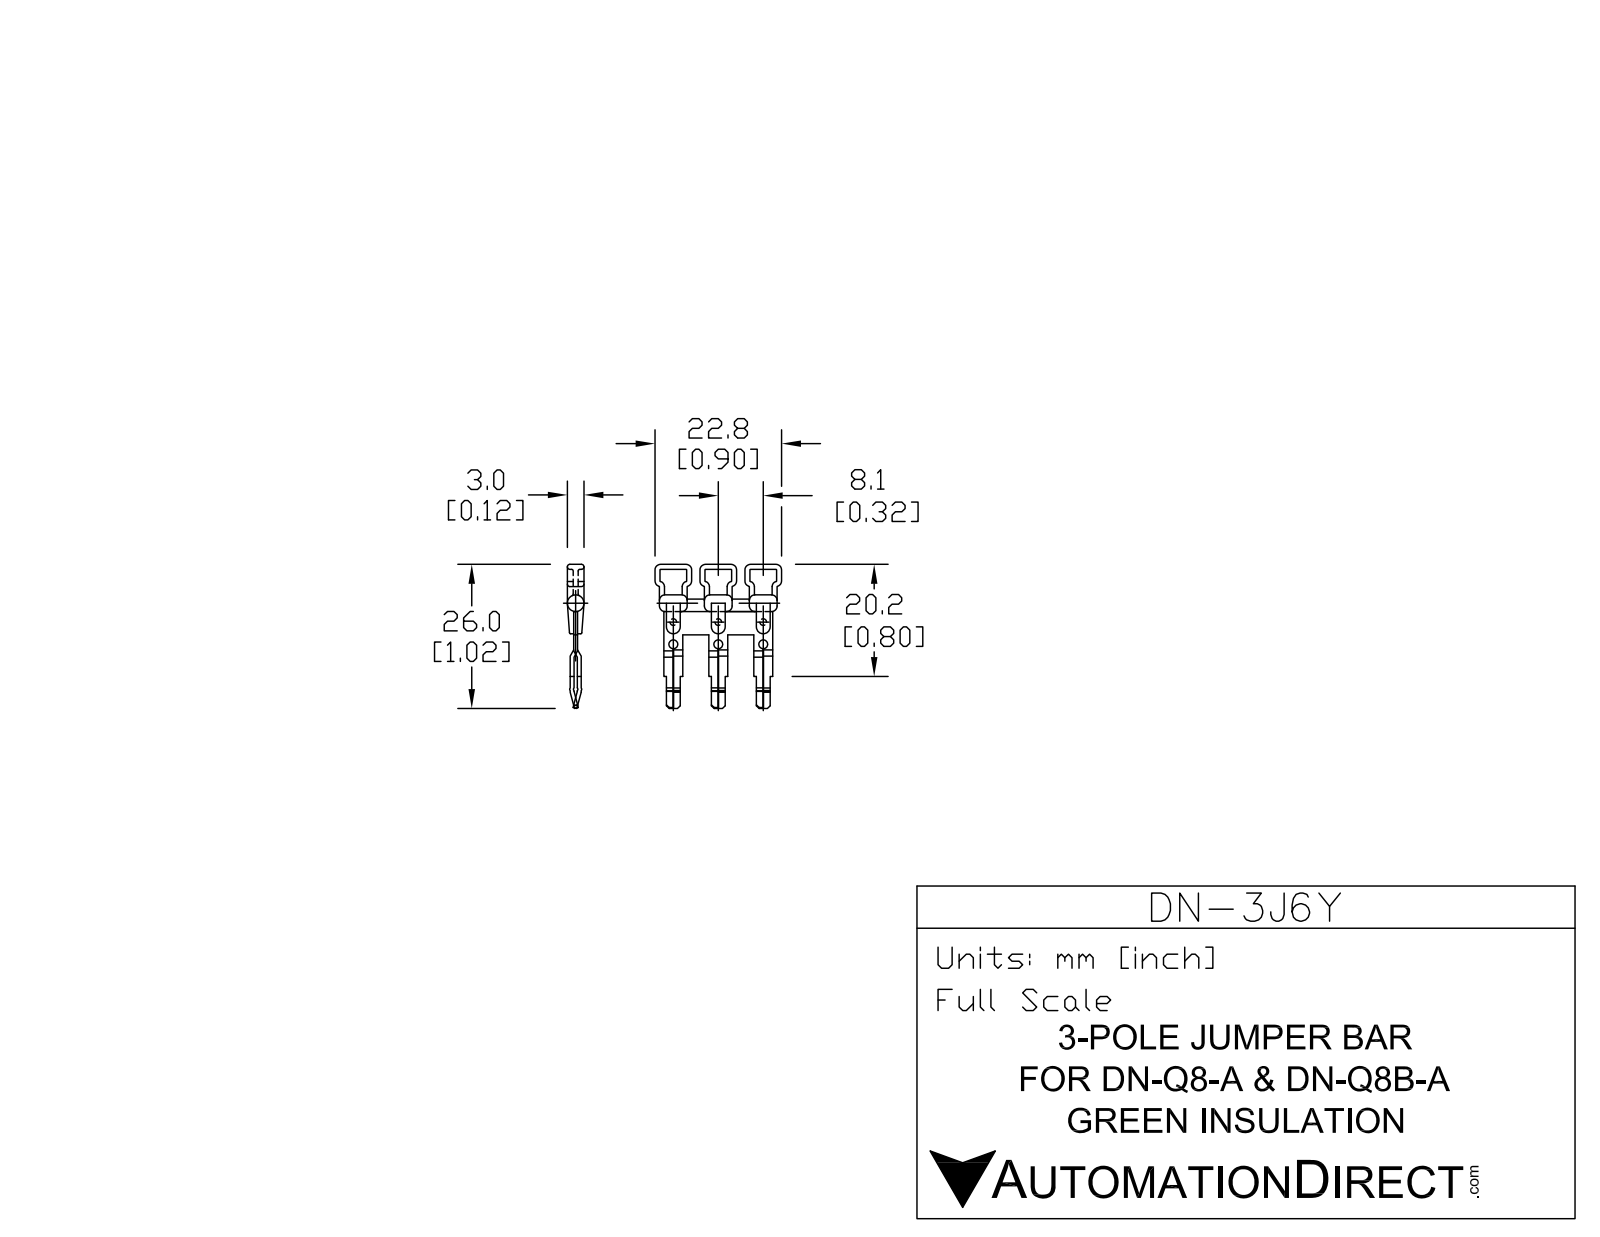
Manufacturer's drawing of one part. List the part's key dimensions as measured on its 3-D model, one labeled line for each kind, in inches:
Part name (STEP PRODUCT): 43530_03_DN-3J6Y
STEP written by: SolidWorks 2013 (AUTOMOTIVE_DESIGN)
Units: inches
Bodies: 2 solids, 531 faces (157 planar, 214 cylindrical, 160 other)
Overall size (bounding box): 1.009 × 0.898 × 0.118
Volume: 0.03 in³ · Surface area: 1.858 in²
Round holes (diameter × count): ⌀0.047 ×3, ⌀0.051 ×3
Round bosses / shafts (diameter × count): ⌀0.118 ×1
Partial cylindrical surfaces — rounded edges, fillets, slot ends (radius × count): R0.008 ×58, R0.028 ×30, R0.039 ×18, R0.004 ×12, R0.02 ×12, R0.075 ×6, R0.049 ×3, R0.03 ×1
Main face-to-face distances: 0.028, 0.022, 0.031, 0.319, 0.035, 0.071, 0.018, 0.049, 0.053, 0.043
Hole centre spacings: 0.319, 0.357, 0.161, 0.638, 0.658
